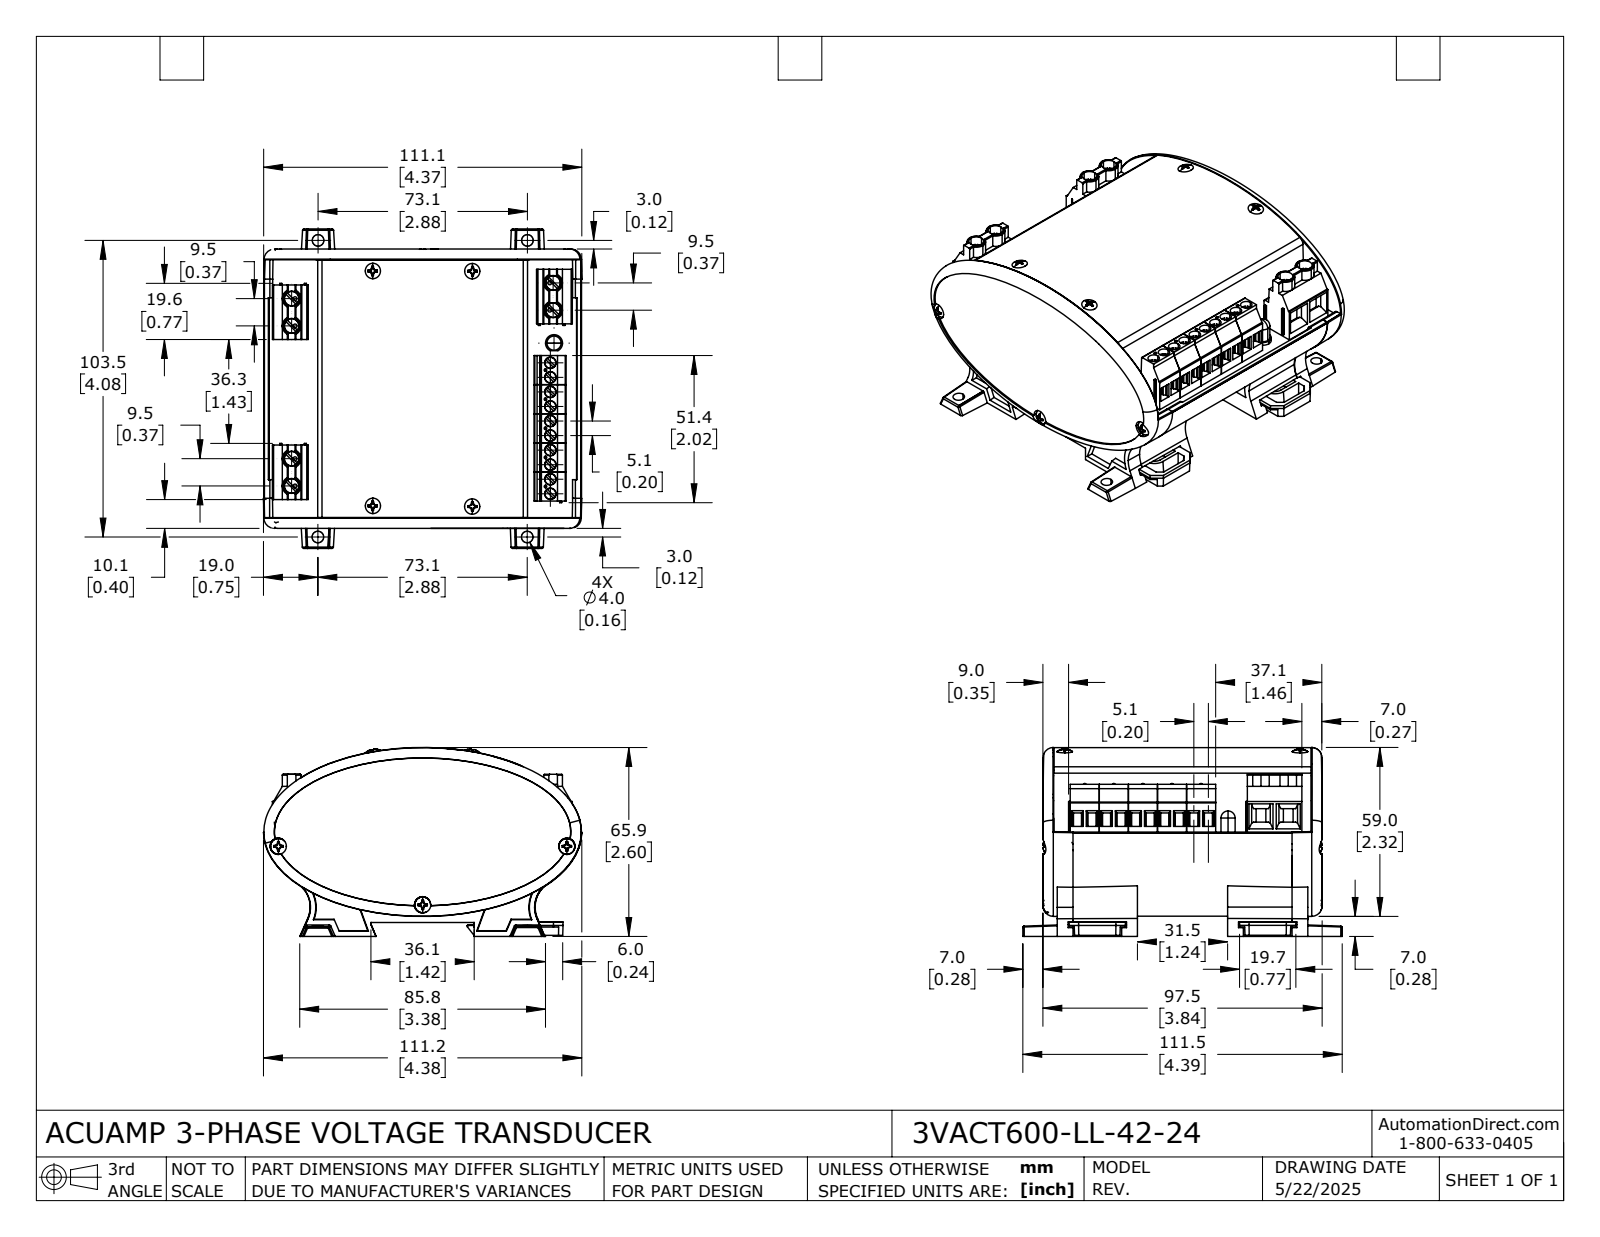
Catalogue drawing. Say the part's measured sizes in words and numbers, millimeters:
The part is named "3VACT600-LL-42-24". Its 3-D file was written by "SolidWorks 2024 (AUTOMOTIVE_DESIGN)". It is 26 solids with 2965 faces: 1484 planar, 838 cylindrical and 643 other. Overall it measures 111.5 by 111.2 by 66 millimeters. Its volume is 139 900 cubic millimeters and its surface area 127 400 square millimeters. Round holes: 12 of diameter 1.3, 10 of diameter 4, 6 of diameter 2, 6 of diameter 2.8, 6 of diameter 5.2, 4 of diameter 3.2. Round bosses or shafts: 16 of diameter 1.3, 10 of diameter 3.8, 10 of diameter 2.8, 10 of diameter 1.7, 6 of diameter 5, 4 of diameter 0.5, 1 of diameter 5.9, 1 of diameter 4.9. Partial cylindrical surfaces (rounded edges, fillets, slot ends): 40 of radius 0.2, 20 of radius 1, 16 of radius 0.2, 16 of radius 0.5, 6 of radius 0.3, 6 of radius 0.3, 6 of radius 3.3, 4 of radius 0.5. The main face-to-face distances are 1.6, 3.3, 93.3, 96.5, 90, 2.1, 10, 86.5, 6.8, 83.3. The hole center spacings are 5.1, 10.2, 15.2, 20.3, 25.4, 30.5, 35.6, 40.6.
